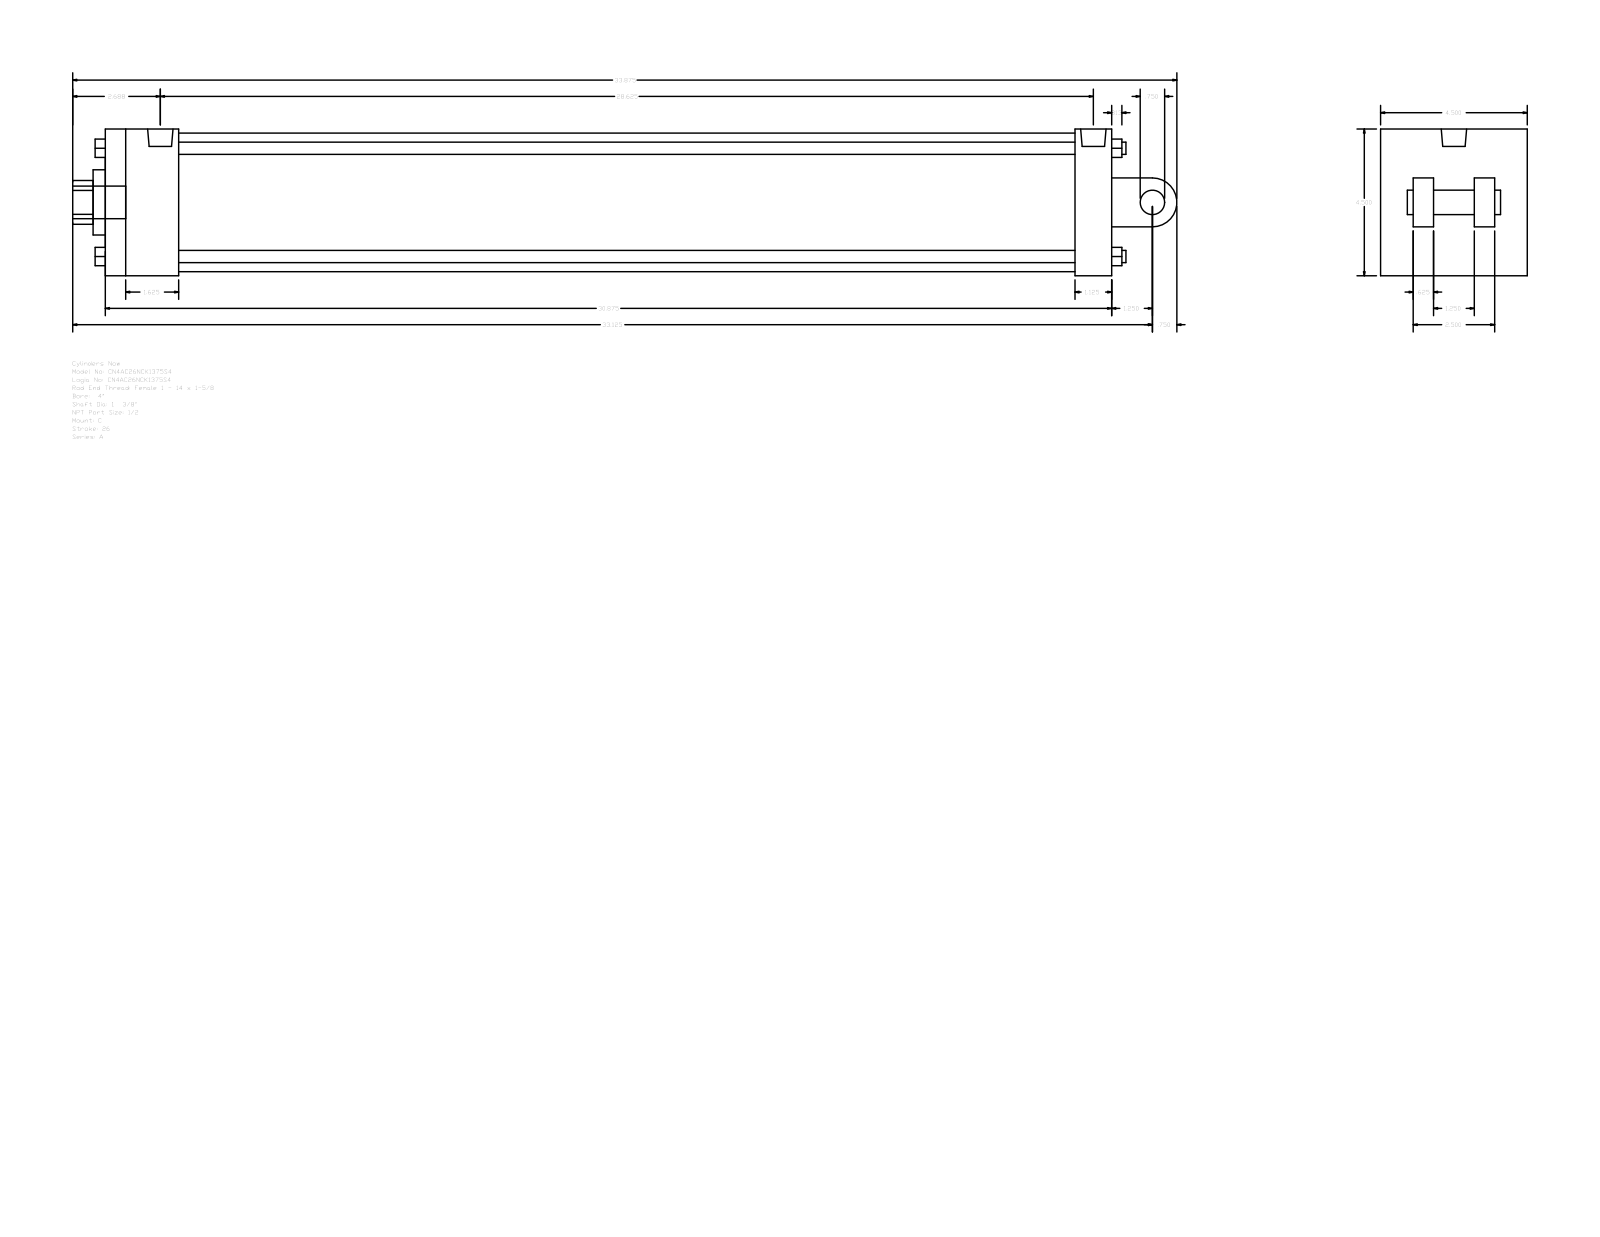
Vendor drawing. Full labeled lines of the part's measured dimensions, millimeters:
Part name (STEP PRODUCT): A_C__0400_1.375
STEP written by: GSSL Pune (CONFIG_CONTROL_DESIGN)
Units: millimetres
Bodies: 0 solids, 135 faces (102 planar, 33 cylindrical, 0 other)
Overall size (bounding box): 860.42 × 114.3 × 114.3
Round holes (diameter × count): ⌀8.73 ×2, ⌀19.77 ×1, ⌀34.92 ×1, ⌀50.8 ×1, ⌀107.95 ×1
Round bosses / shafts (diameter × count): ⌀9.53 ×4, ⌀8.73 ×2, ⌀25.4 ×1, ⌀19.77 ×1, ⌀19.05 ×1
Partial cylindrical surfaces — rounded edges, fillets, slot ends (radius × count): R17.06 ×1, R19.05 ×1
Main face-to-face distances: 114.3, 784.22, 73.03, 28.57, 755.65, 57.15, 698.5, 727.07, 15.87, 41.27
Hole centre spacings: 3.18
